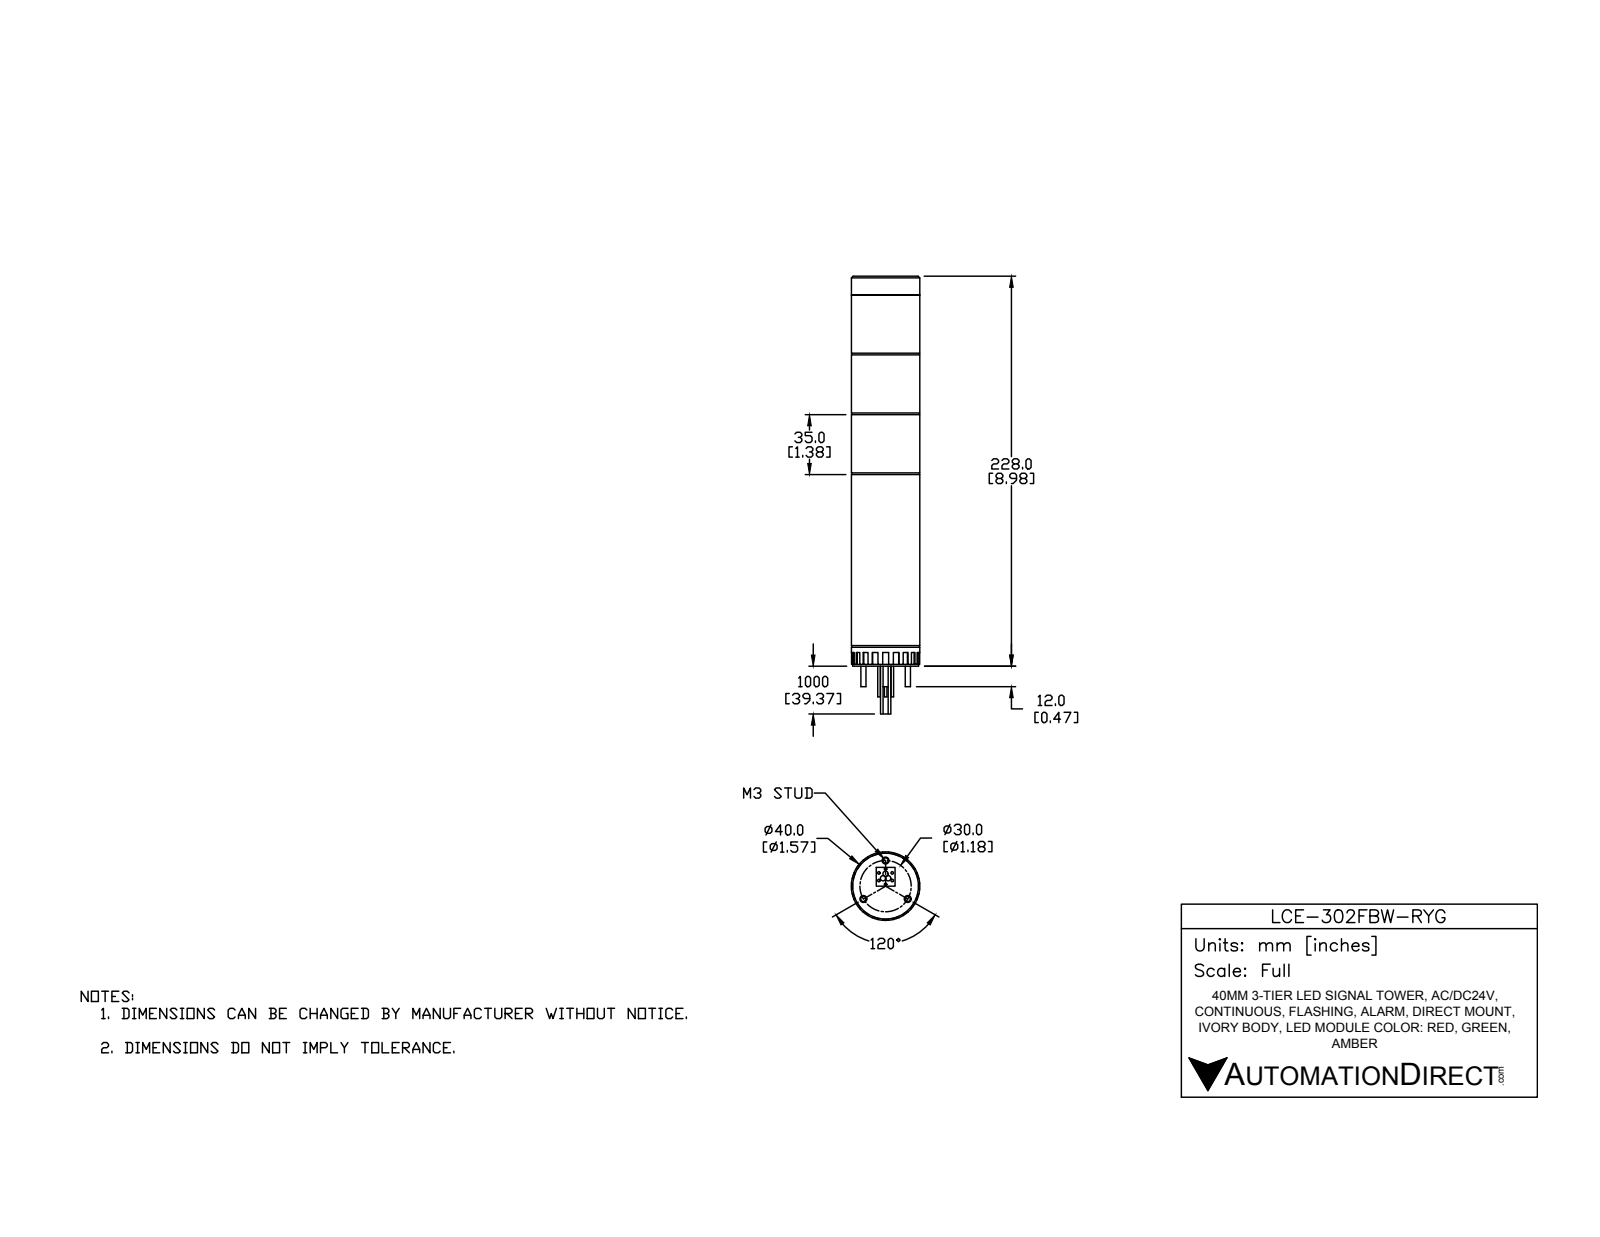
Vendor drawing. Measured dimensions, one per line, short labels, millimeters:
name: LCE-302FBW-RYG
written by: SolidWorks 2016 (AUTOMOTIVE_DESIGN)
unit: mm
bodies: 25 solids, 218 faces (156 planar, 58 cylindrical, 4 other)
size: 246 × 40 × 40
volume: 285 101 mm³; area: 57 726 mm²
holes: 3× ⌀4, 1× ⌀8
bosses: 10× ⌀1.5, 3× ⌀3, 1× ⌀40, 1× ⌀39.5, 1× ⌀38.5, 1× ⌀5.5
face distances: 35, 1, 70, 34, 36, 69, 101, 136, 171, 11
hole spacings: 15, 25.98
